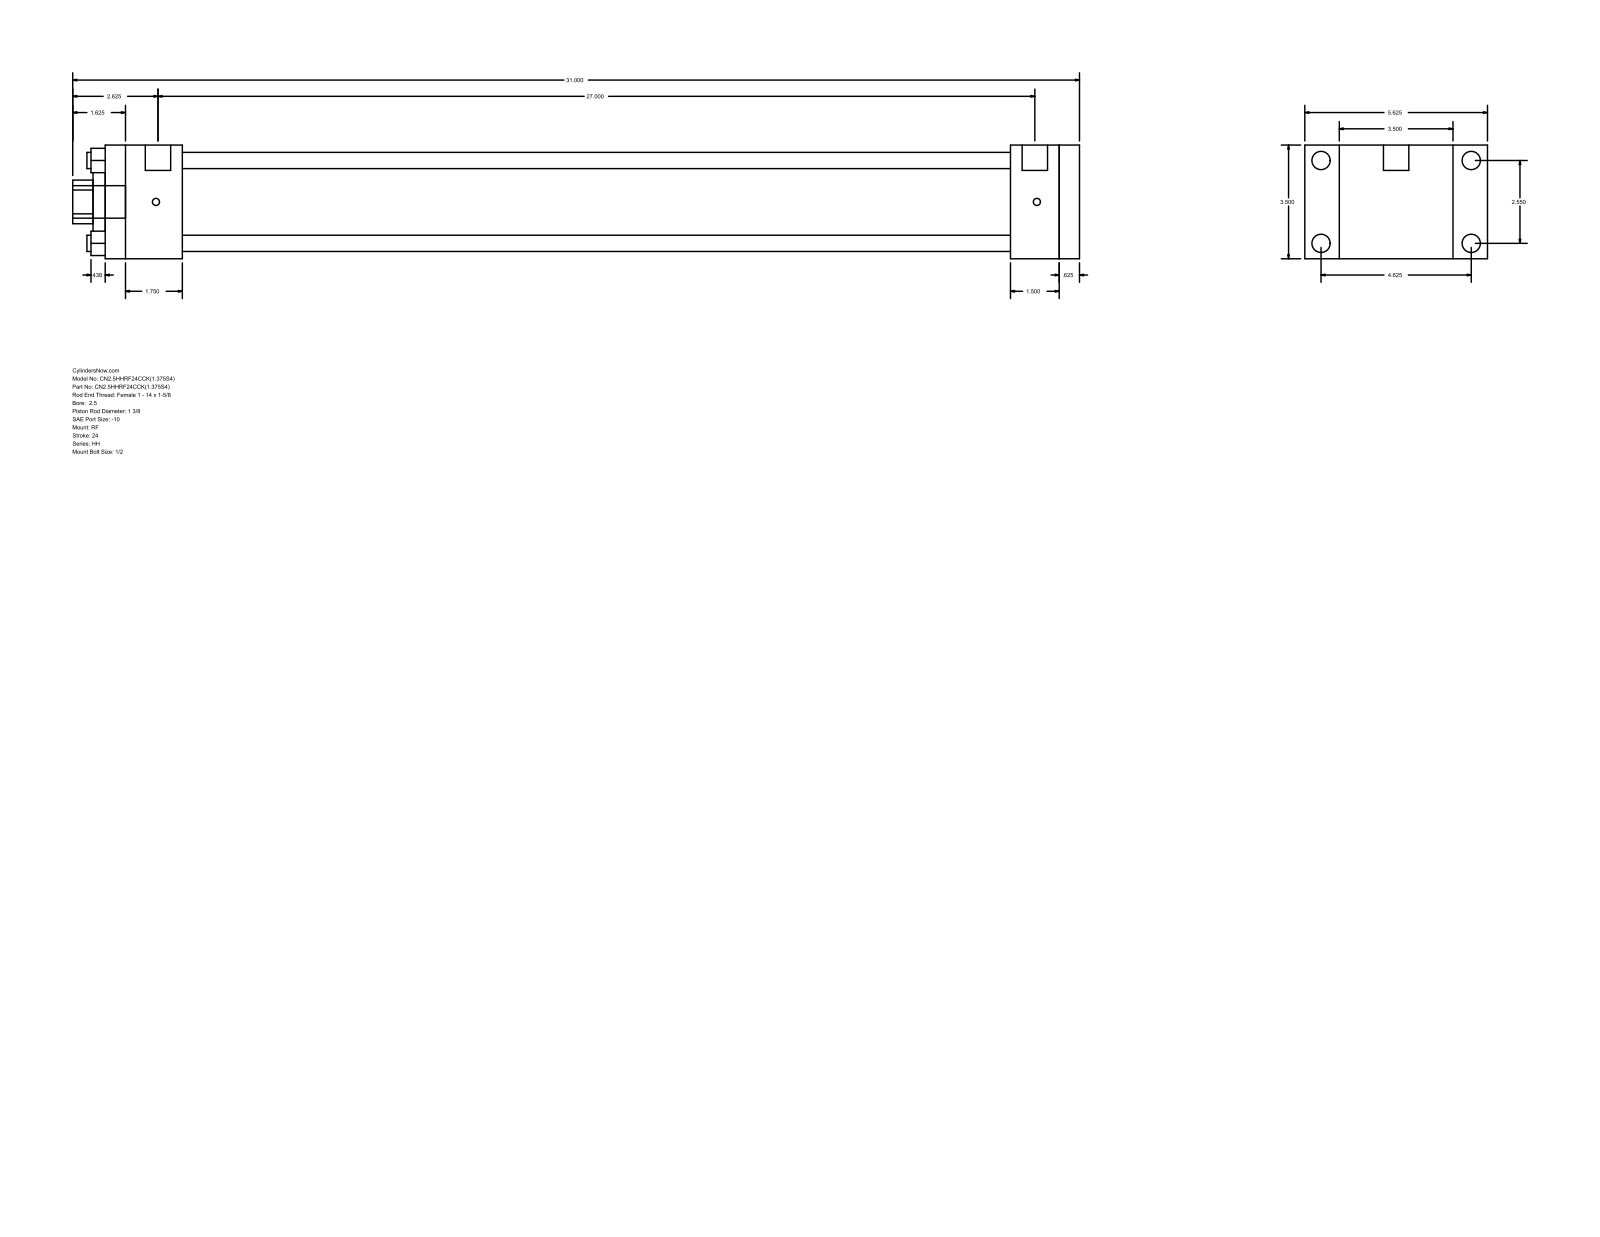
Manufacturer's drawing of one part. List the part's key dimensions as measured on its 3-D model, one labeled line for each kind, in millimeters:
Part name (STEP PRODUCT): HH_RF__0250_1.375
STEP written by: GSSL Pune (CONFIG_CONTROL_DESIGN)
Units: millimetres
Bodies: 0 solids, 92 faces (64 planar, 28 cylindrical, 0 other)
Overall size (bounding box): 787.4 × 142.88 × 88.9
Round holes (diameter × count): ⌀12.7 ×4, ⌀34.92 ×1, ⌀50.8 ×1, ⌀73.03 ×1
Round bosses / shafts (diameter × count): ⌀14.3 ×4, ⌀5.56 ×4, ⌀19.84 ×2, ⌀25.4 ×1
Partial cylindrical surfaces — rounded edges, fillets, slot ends (radius × count): R17.06 ×1
Main face-to-face distances: 88.9, 762, 15.88, 746.12, 60.32, 685.8, 701.68, 708.02, 647.7, 38.1
Hole centre spacings: 45.79, 64.76, 91.58
